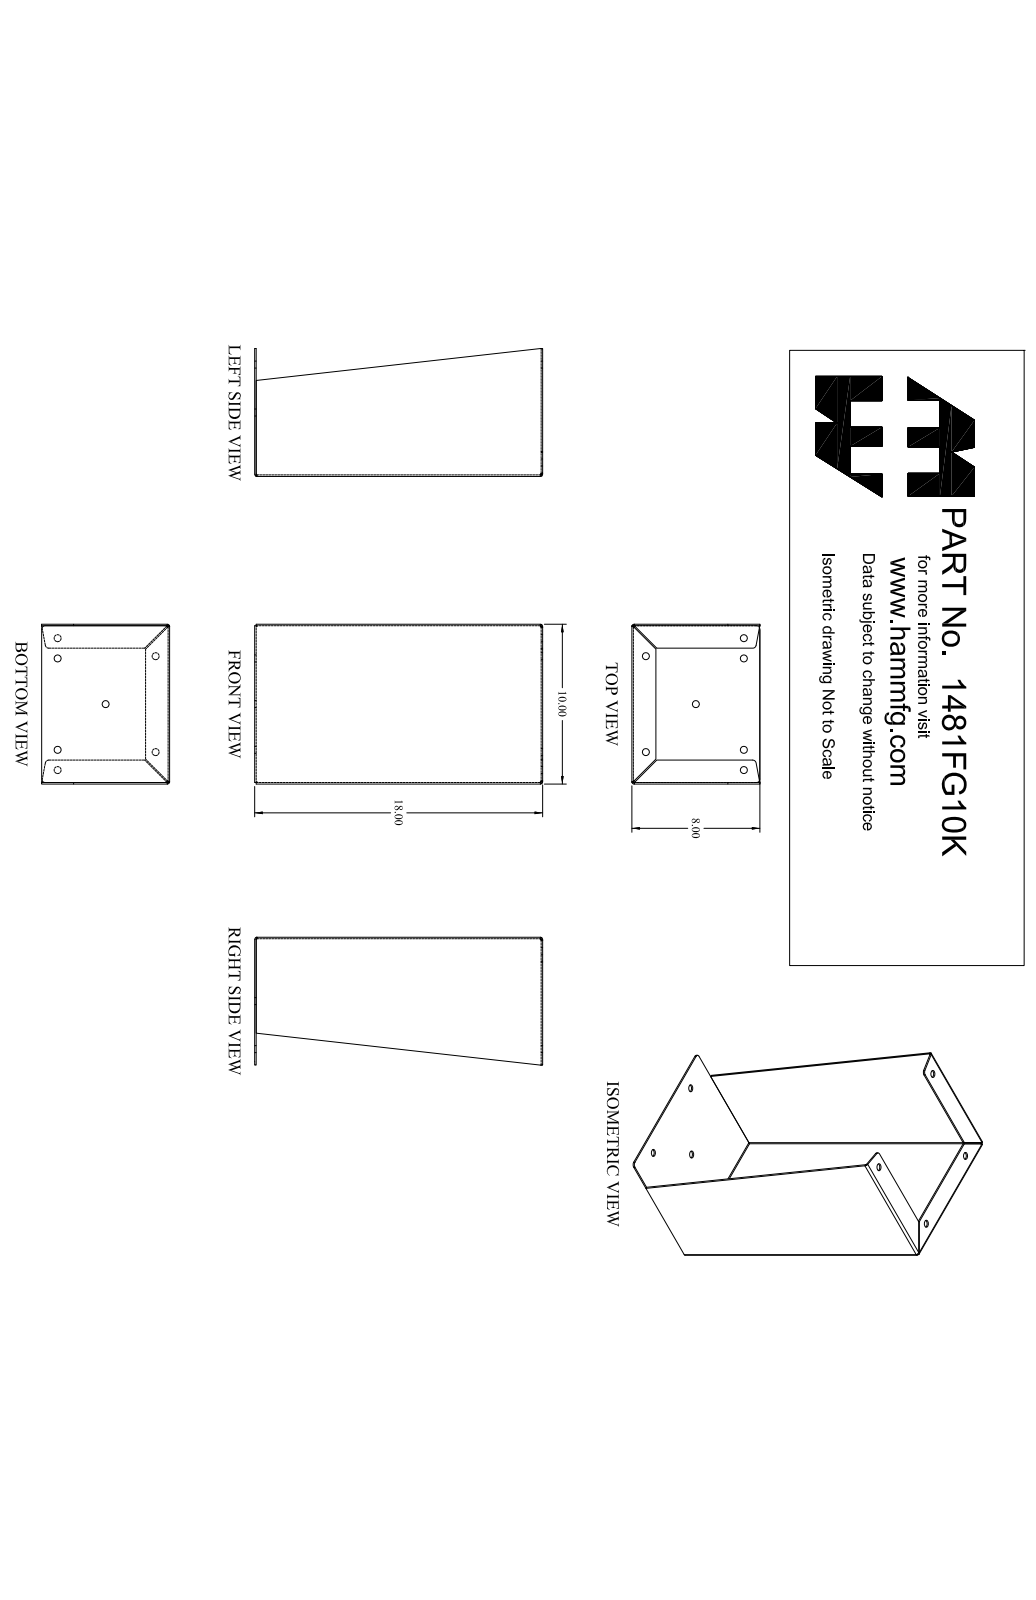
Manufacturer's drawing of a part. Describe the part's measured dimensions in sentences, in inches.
The part is named "1481FG10K_Default". Its 3-D file was written by "SolidWorks 2019 (CONFIG_CONTROL_DESIGN)". It is 1 solid with 78 faces: 42 planar, 30 cylindrical and 6 other. Overall it measures 18 by 10 by 8 inches. Its volume is 50.58 cubic inches and its surface area 1 076 square inches. Round holes: 7 of diameter 0.437. Partial cylindrical surfaces (rounded edges, fillets, slot ends): 6 of radius 0.048, 6 of radius 0.143, 4 of radius 0.22. The main face-to-face distances are 0.095, 9.905, 10, 9.81, 0.095, 17.81, 17.905, 17.905, 18, 1.405. The hole center spacings are 1.266, 4.144, 4.331, 5.101, 6.126, 6.227, 6.984, 8.476.
